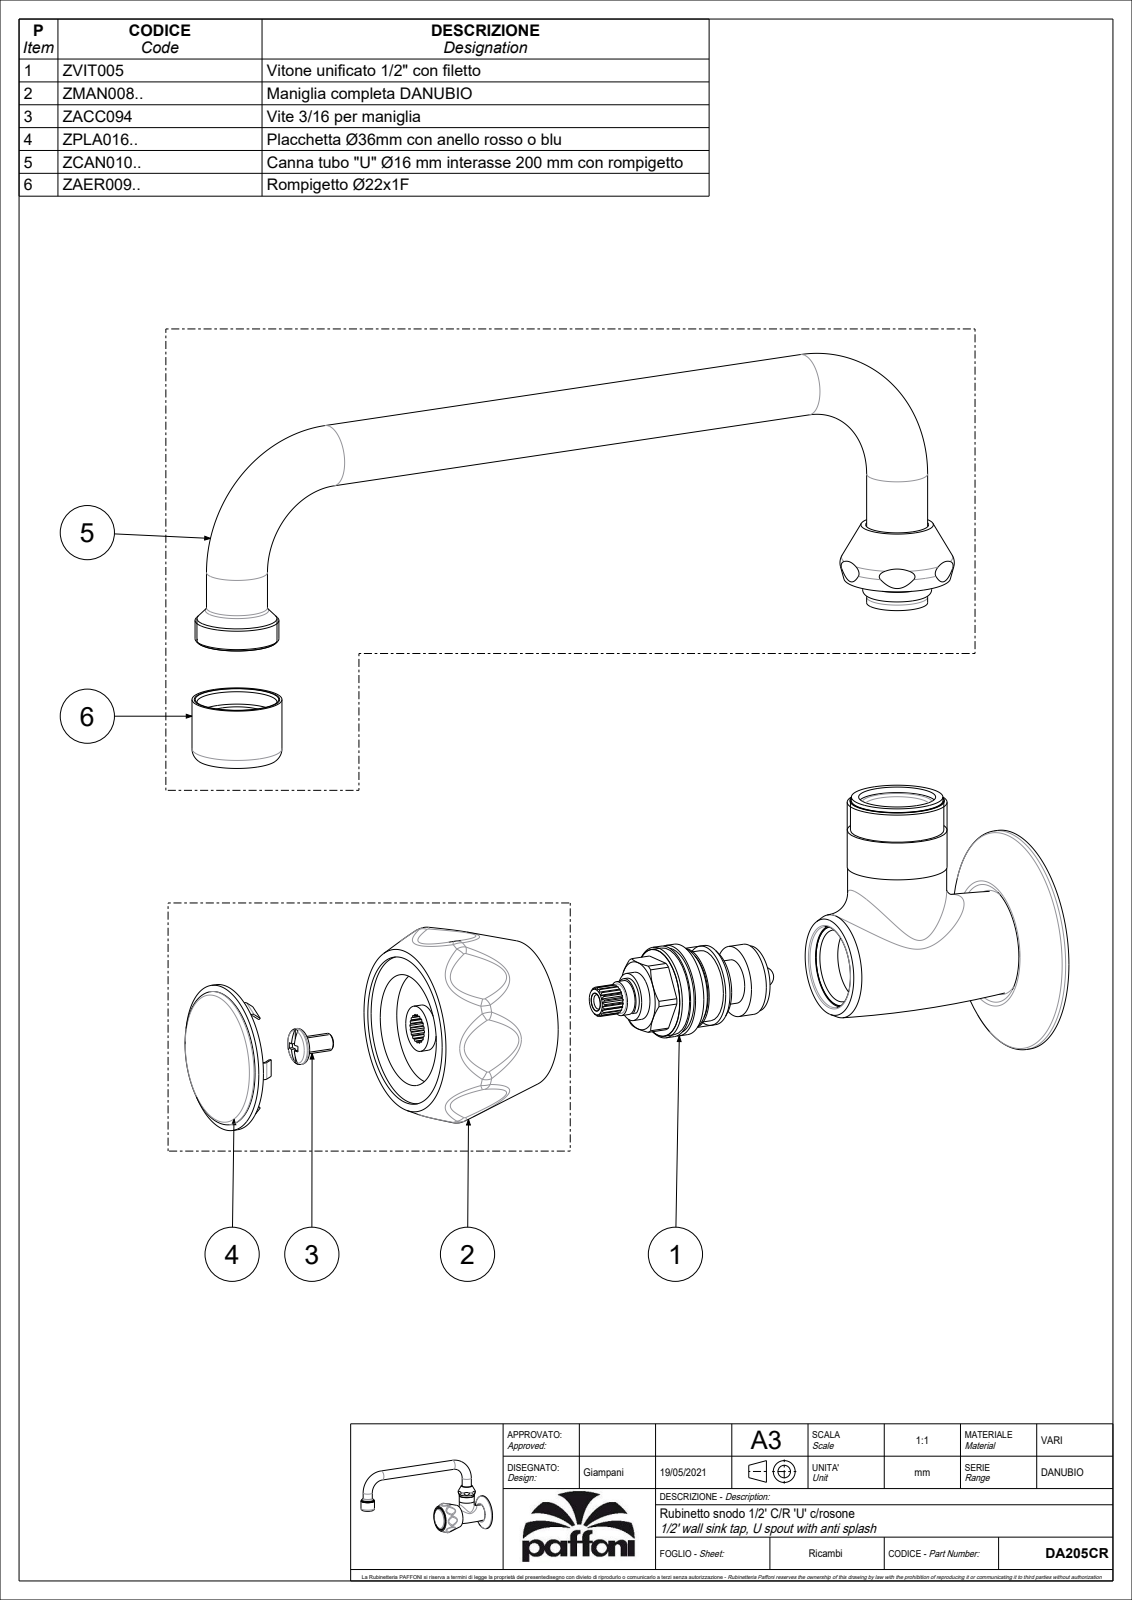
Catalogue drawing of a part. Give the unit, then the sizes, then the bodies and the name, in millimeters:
Units: millimetres
Overall size (bounding box): 253.8 × 131.3 × 58
Round bosses / shafts (diameter × count): ⌀16 ×3, ⌀58 ×1, ⌀38.5 ×1, ⌀26.2 ×1, ⌀26 ×1, ⌀23.6 ×1, ⌀22 ×1, ⌀21 ×1
Partial cylindrical surfaces — rounded edges, fillets, slot ends (radius × count): R21.31 ×8
Main face-to-face distances: 54.1, 89.4, 35.3, 6.7, 60.8, 96.1, 96.5, 89.8, 35.7, 0.4
Volume: 188 328 mm³ · Surface area: 35 512 mm²
Bodies: 1 solid, 136 faces (16 planar, 28 cylindrical, 92 other)
Part name (STEP PRODUCT): DA205CR
STEP written by: CREO PARAMETRIC BY PTC INC, 2020044 (CONFIG_CONTROL_DESIGN)
